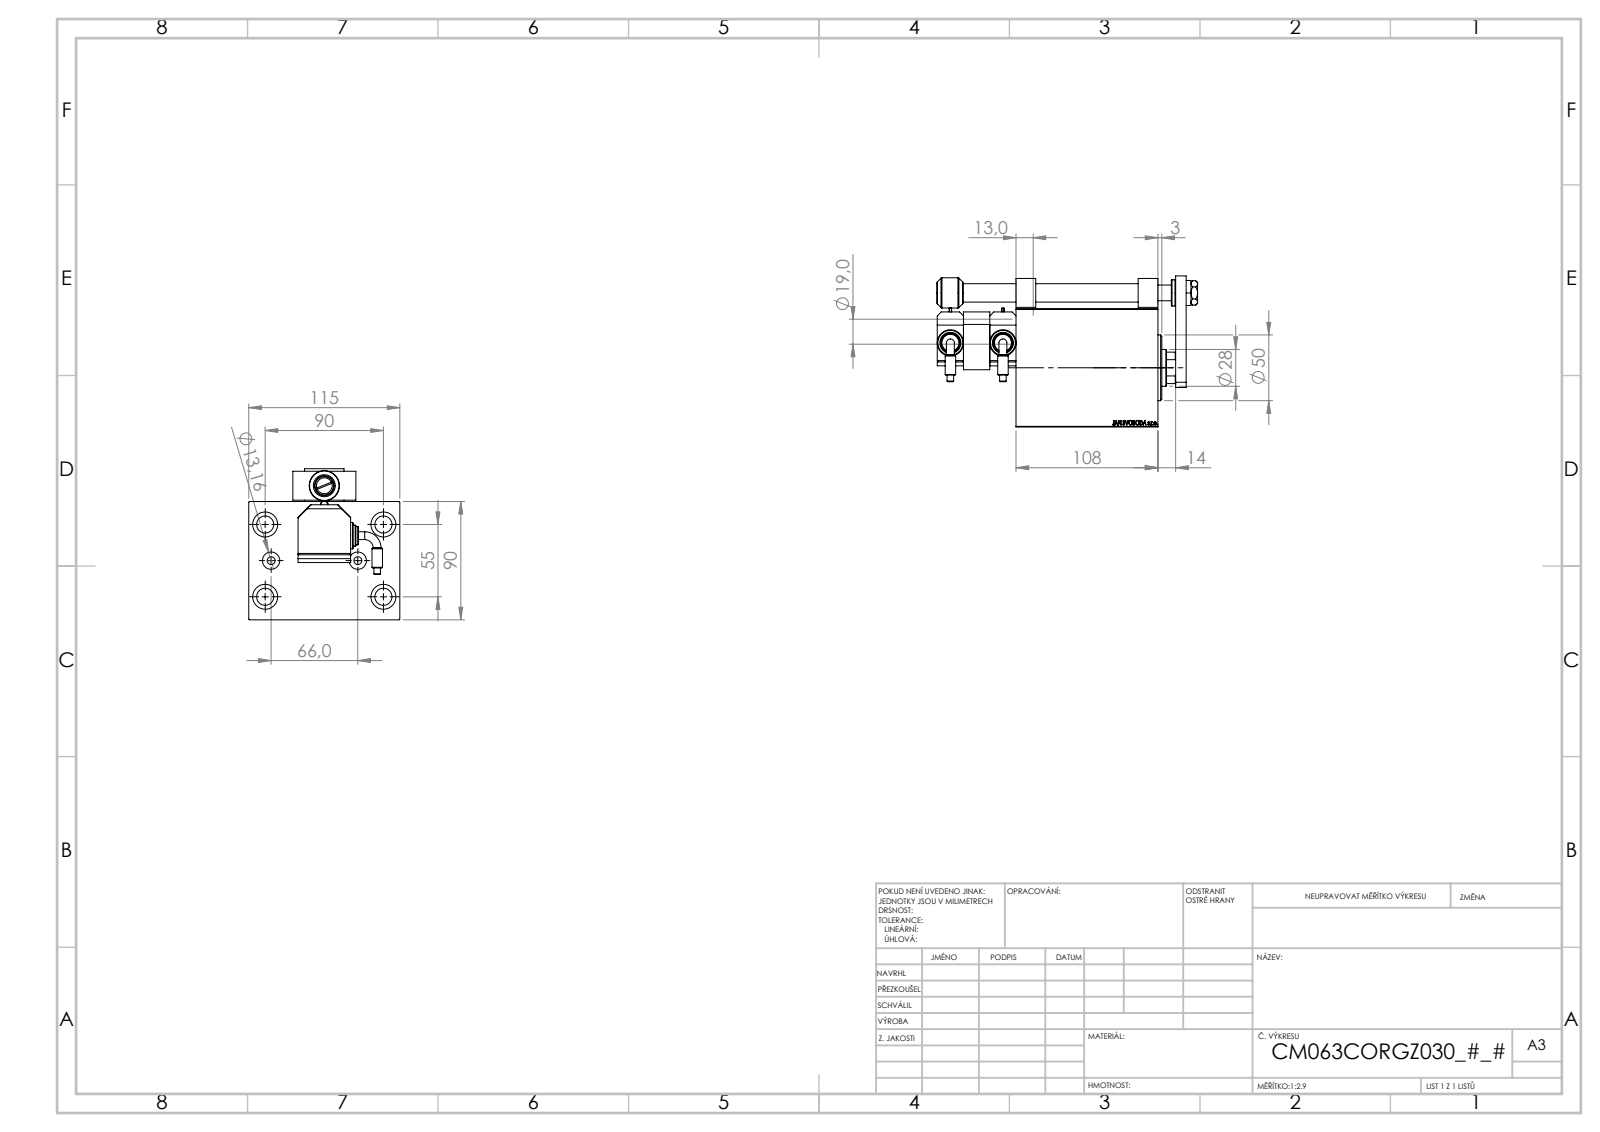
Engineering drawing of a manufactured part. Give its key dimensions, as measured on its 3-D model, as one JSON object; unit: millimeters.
{"part_name": "SWITCH_P_FRONT_BACK; ZARAZKA_P; MIDDLE; V450CM_C_Body (+8 more)", "step_written_by": "SolidWorks 2019 (CONFIG_CONTROL_DESIGN)", "units": "millimeters", "bodies": {"solids": 14, "faces": 1114, "planar": 525, "cylindrical": 124, "other": 465}, "overall_size": [198.5, 115, 115], "volume_mm3": 1144000, "surface_area_mm2": 191257, "round_holes": [[13, 5], [4, 4], [8, 4], [19, 4], [6, 2], [13.16, 2], [12, 1], [14, 1], [18.5, 1], [20, 1], [28, 1], [31.5, 1]], "round_bosses_or_shafts": [[20, 3], [16, 2], [14, 2], [8, 2], [6, 2], [5.04, 2], [50, 1], [23, 1]], "partial_cylinders_radius": [[3, 1], [13.5, 1]], "face_to_face_distances": [90, 115, 108, 20, 19, 89, 40, 39, 8, 30], "hole_center_spacings": [30, 52.74, 82.71, 20, 33, 53.81, 55, 65.86]}
